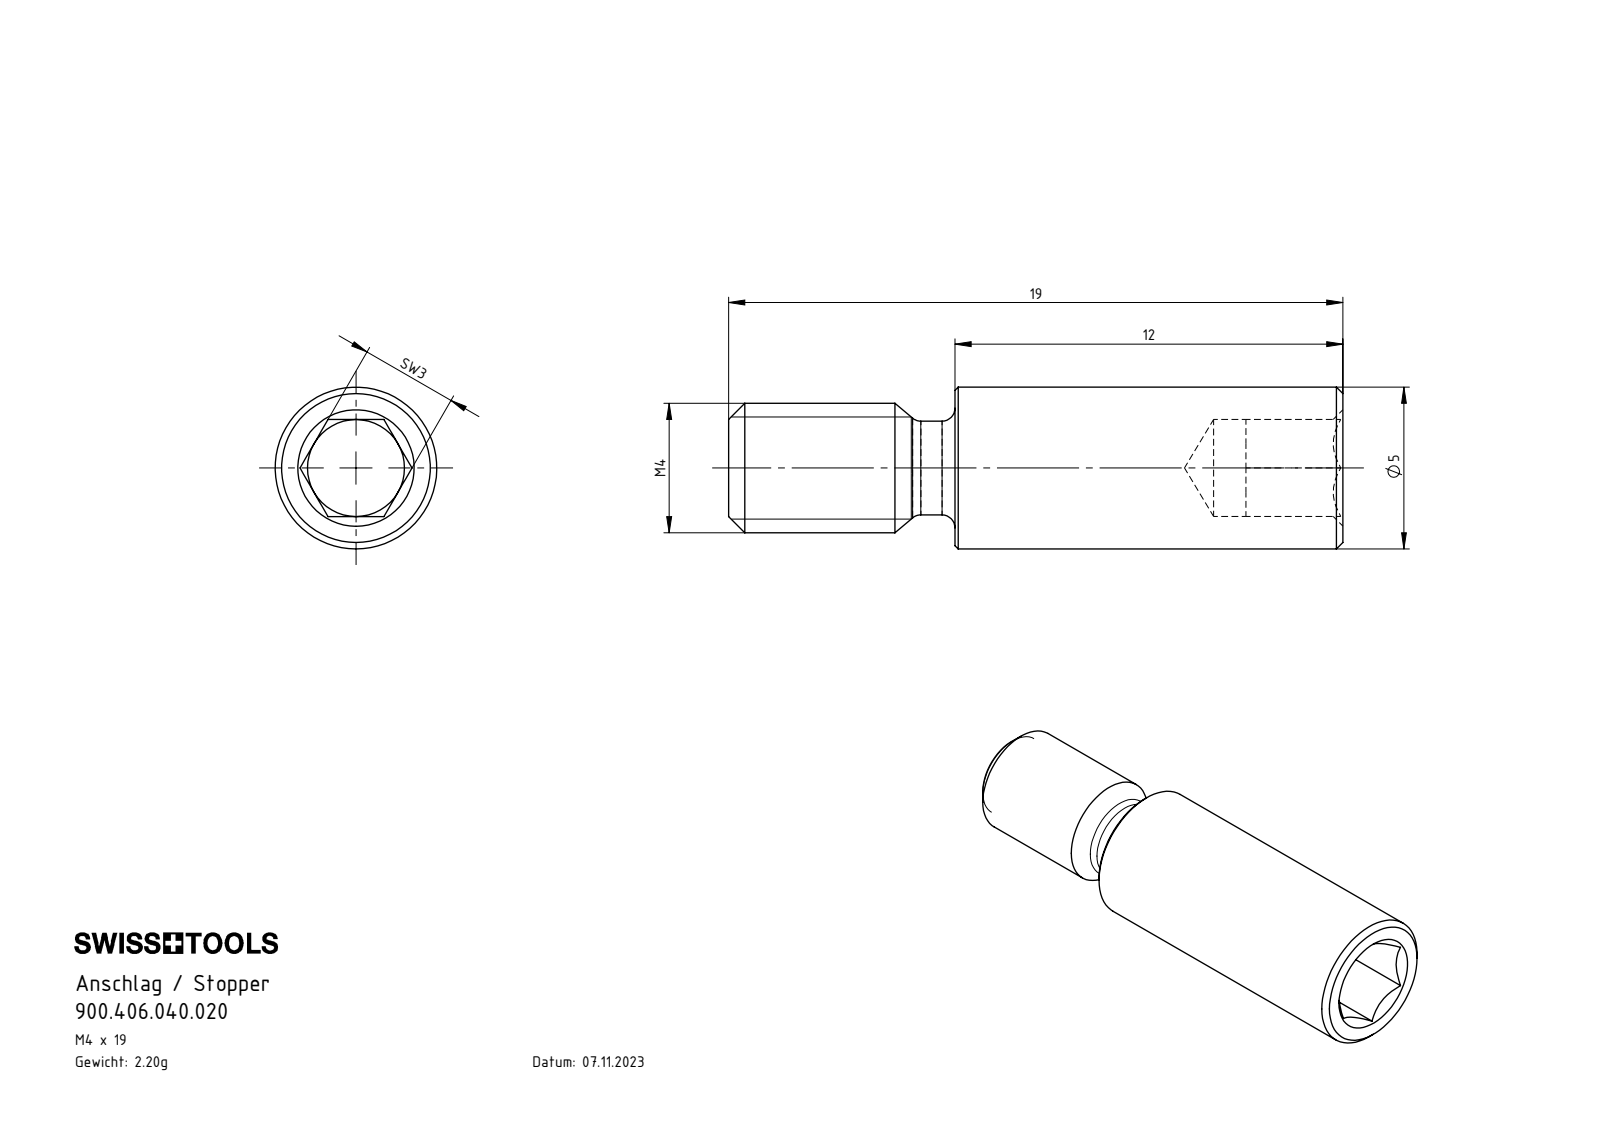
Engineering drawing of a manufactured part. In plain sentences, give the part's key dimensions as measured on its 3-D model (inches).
The part is named "900.406.040.020". Its 3-D file was written by "SolidWorks 2022 (AUTOMOTIVE_DESIGN)". It is 1 solid with 39 faces: 15 planar, 8 cylindrical and 16 other. Overall it measures 0.748 by 0.197 by 0.197 inches. Its volume is 0.017 cubic inches and its surface area 0.544 square inches. Round holes: 1 of diameter 0.118. Round bosses or shafts: 1 of diameter 0.197, 1 of diameter 0.157, 1 of diameter 0.114. The main face-to-face distances are 0.118, 0.276, 0.748, 0.472, 0.63, 0.354.
